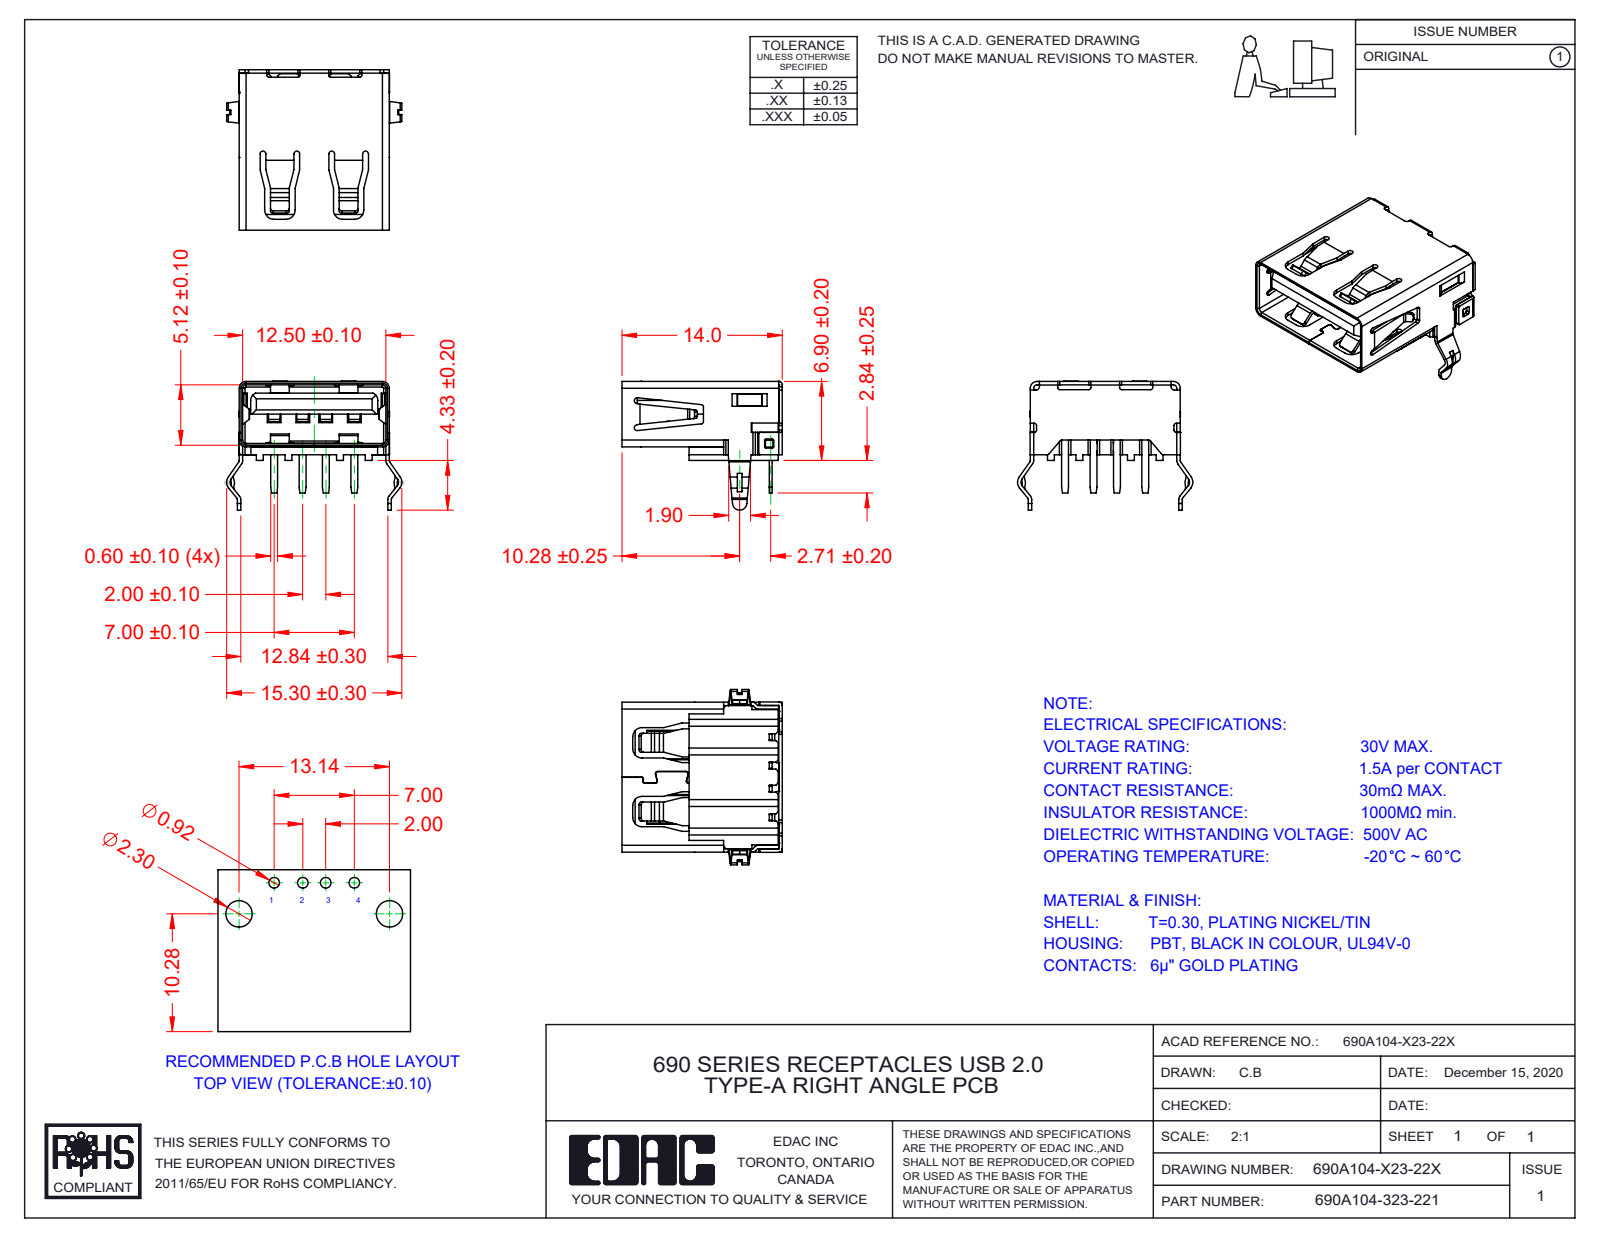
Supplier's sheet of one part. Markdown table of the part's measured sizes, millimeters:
| quantity | value |
| --- | --- |
| part name | 690A104-123-221; Contact 690A104-X23-22X; Insulator 690A104-X23-22X_Black; Shell 690A104-X23-22X |
| STEP written by | SolidWorks 2020 (AUTOMOTIVE_DESIGN) |
| units | millimeters |
| bodies | 6 solids, 878 faces (658 planar, 210 cylindrical, 10 other) |
| overall size | 15.3 × 14 × 11.25 |
| volume | 574 mm³ |
| surface area | 2 130 mm² |
| partial cylindrical surfaces (radius × count) | 0.2 × 34, 0.25 × 17, 0.3 × 16, 0.5 × 16, 0.15 × 12, 0.1 × 10, 0.18 × 8, 0.8 × 6 |
| main face-to-face distances | 5.42, 2.56, 4.83, 2.86, 12.8, 0.72, 1.02, 4.7, 5.72, 4.15 |
